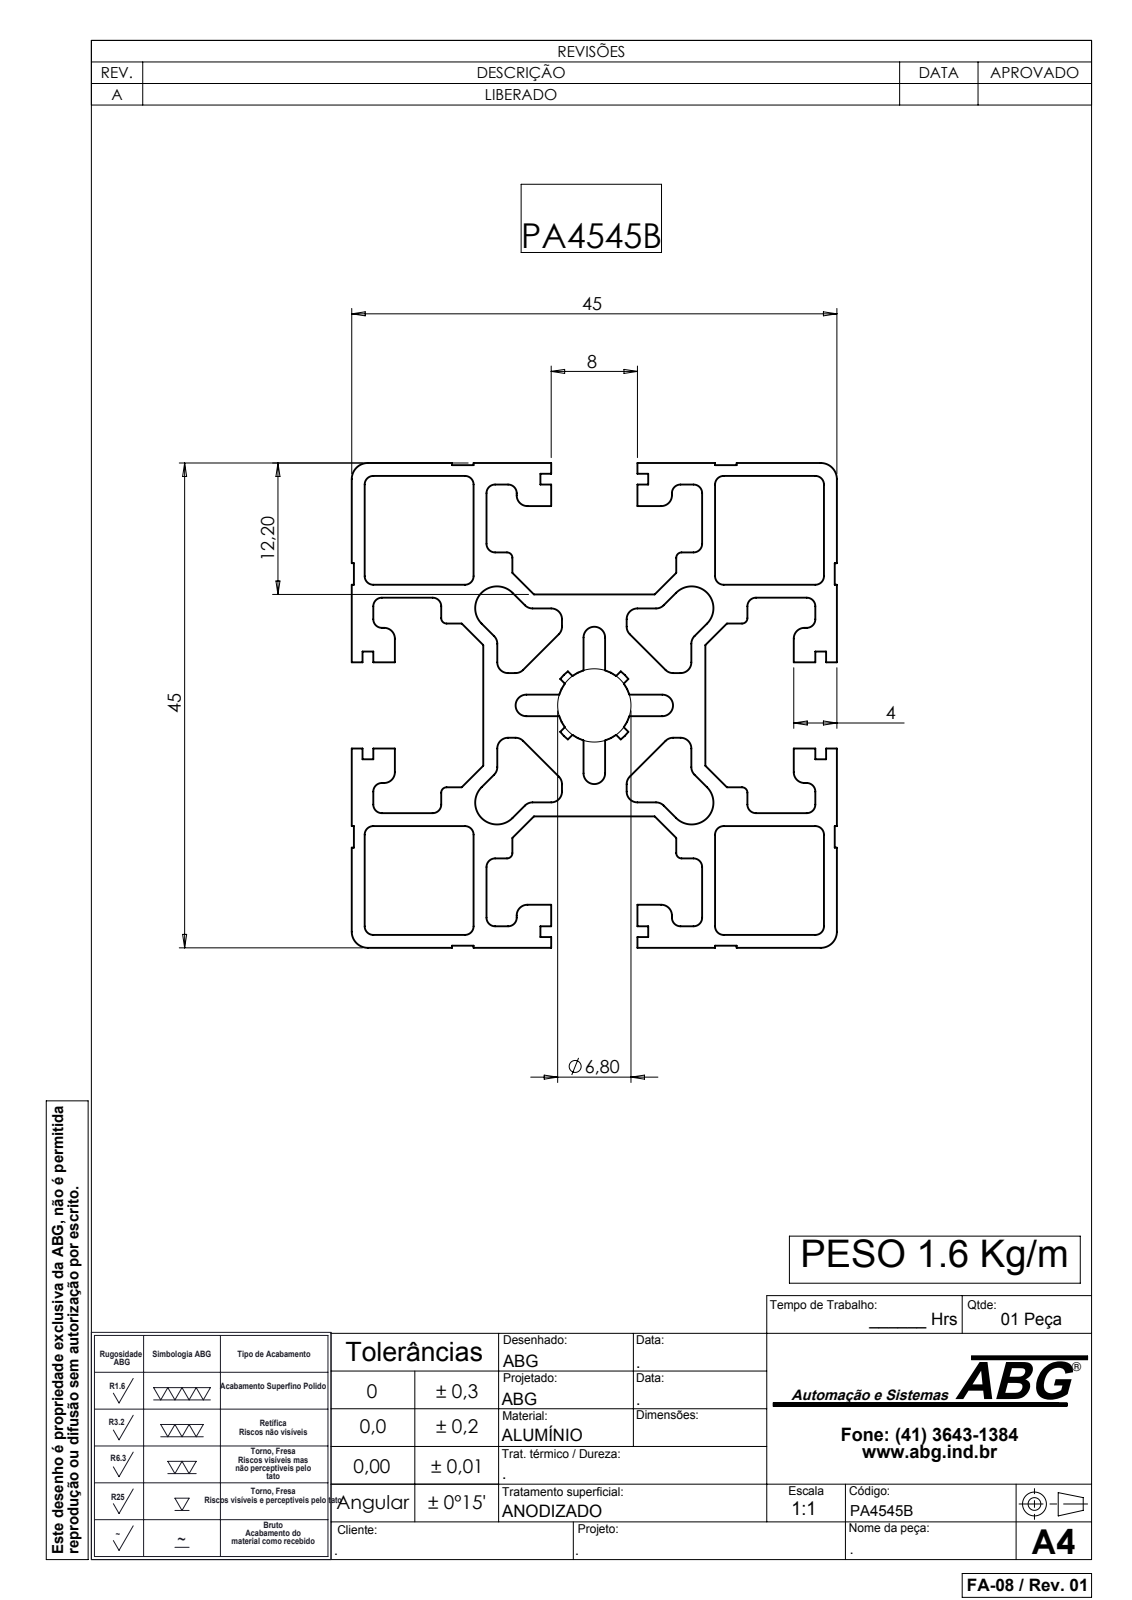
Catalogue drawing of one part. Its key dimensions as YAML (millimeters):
part_name: "PA4545B"
step_written_by: "SolidWorks 2007 (CONFIG_CONTROL_DESIGN)"
units: millimeters
bodies: {solids: 1, faces: 321, planar: 226, cylindrical: 95, other: 0}
overall_size: [6000, 45, 45]
volume: 3877000
surface_area: 4275000
partial_cylinders:
  - {radius: 0.8, count: 40}
  - {radius: 1, count: 36}
  - {radius: 0.5, count: 8}
  - {radius: 1.5, count: 4}
  - {radius: 2.02, count: 4}
face_to_face_distances: [11.3, 1.2, 32.5, 21.5, 33.7, 12.2, 11, 43.8, 10.1, 20.3]
